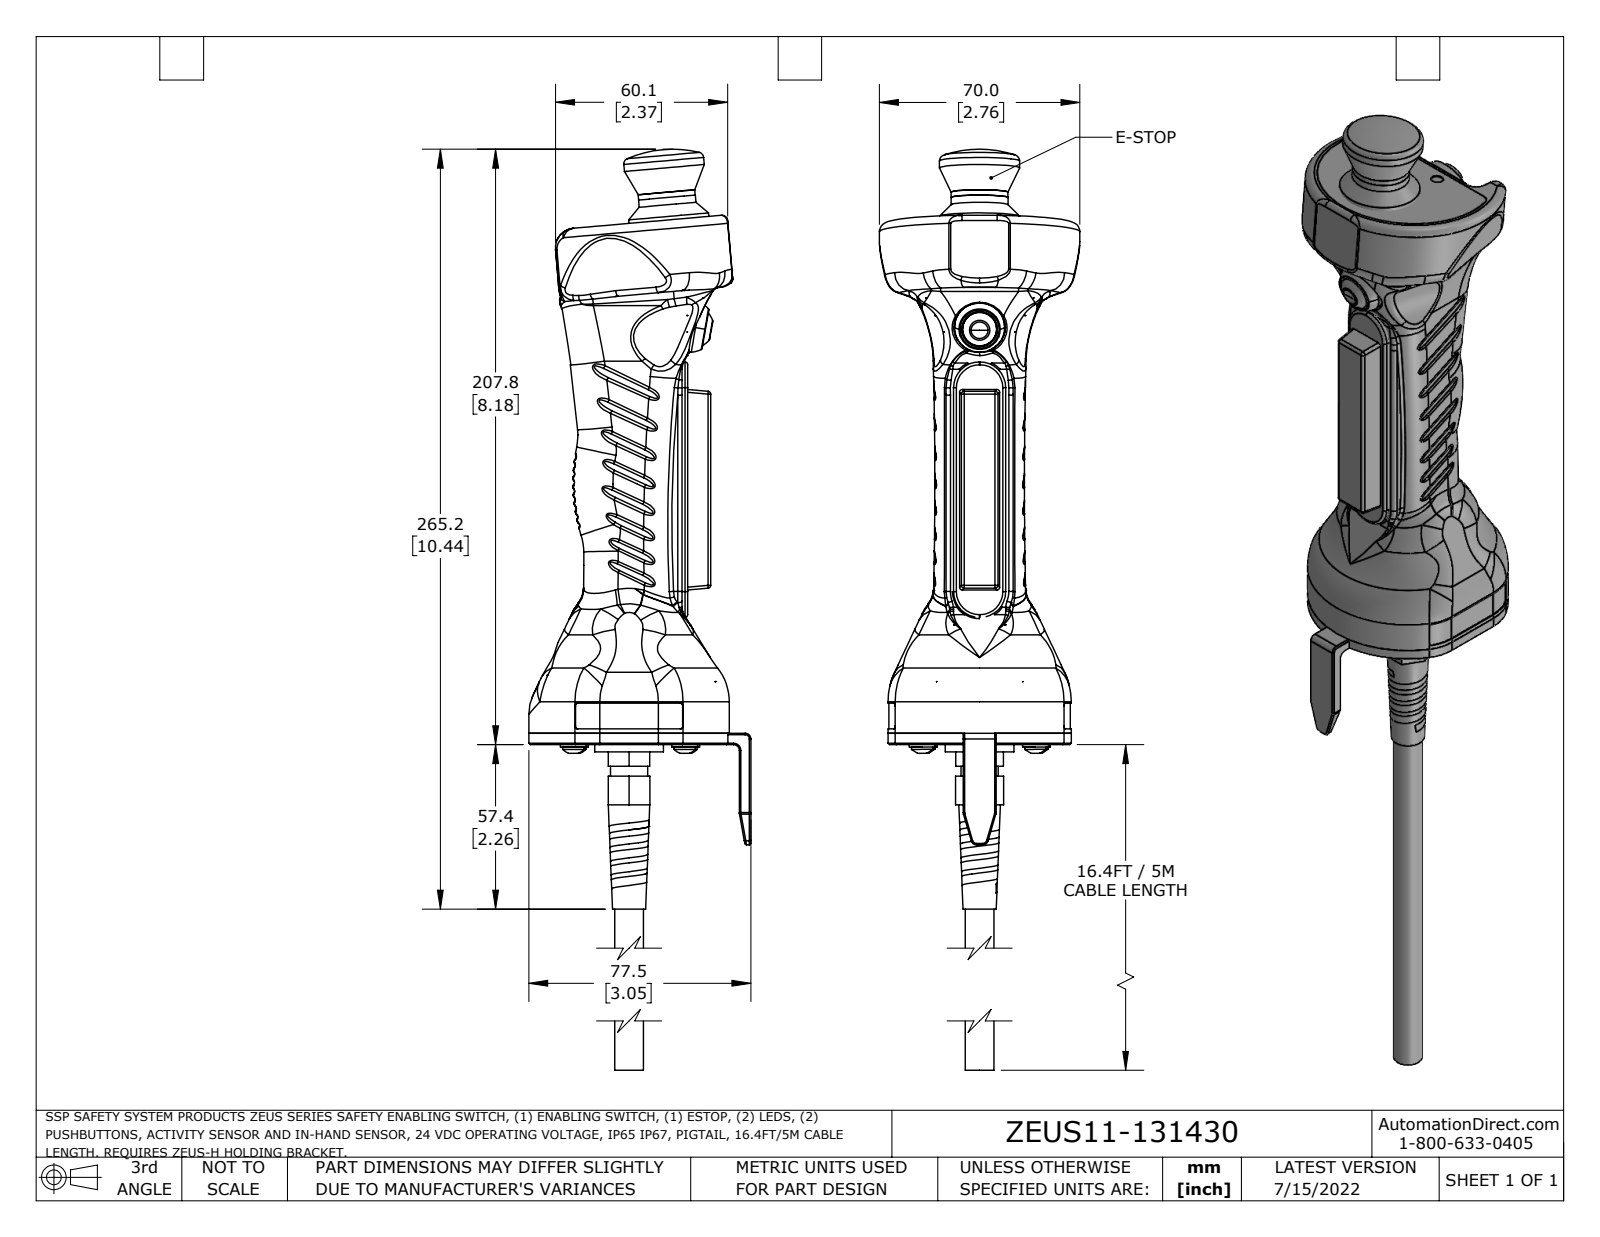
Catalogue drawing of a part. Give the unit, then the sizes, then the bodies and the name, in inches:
Units: inches
Overall size (bounding box): 15.833 × 3.052 × 2.756
Round holes (diameter × count): ⌀0.132 ×4, ⌀0.169 ×4, ⌀0.177 ×4, ⌀0.197 ×4, ⌀0.039 ×2, ⌀0.098 ×2, ⌀0.11 ×2, ⌀0.159 ×2, ⌀0.165 ×2, ⌀0.173 ×2, ⌀0.201 ×2, ⌀0.205 ×2
Round bosses / shafts (diameter × count): ⌀0.354 ×4, ⌀0.295 ×4, ⌀0.157 ×4, ⌀0.039 ×4, ⌀0.461 ×3, ⌀1.102 ×2, ⌀0.781 ×2, ⌀0.689 ×2
Partial cylindrical surfaces — rounded edges, fillets, slot ends (radius × count): R0.005 ×96, R0.039 ×51, R0.028 ×48, R0.008 ×42, R0.079 ×27, R0.006 ×16, R0.118 ×10, R0.031 ×7
Main face-to-face distances: 0.157, 0.079, 0.02, 0.014, 0.065, 0.059, 0.098, 0.039, 0.177, 0.472
Hole centre spacings: 0.404, 0.63, 0.867, 1.08, 1.181, 1.531, 1.558, 0.513
Volume: 24.9 in³ · Surface area: 141.7 in²
Bodies: 22 solids, 1671 faces (650 planar, 525 cylindrical, 496 other)
Part name (STEP PRODUCT): ZEUS11-131430
STEP written by: SolidWorks 2021 (AUTOMOTIVE_DESIGN)
